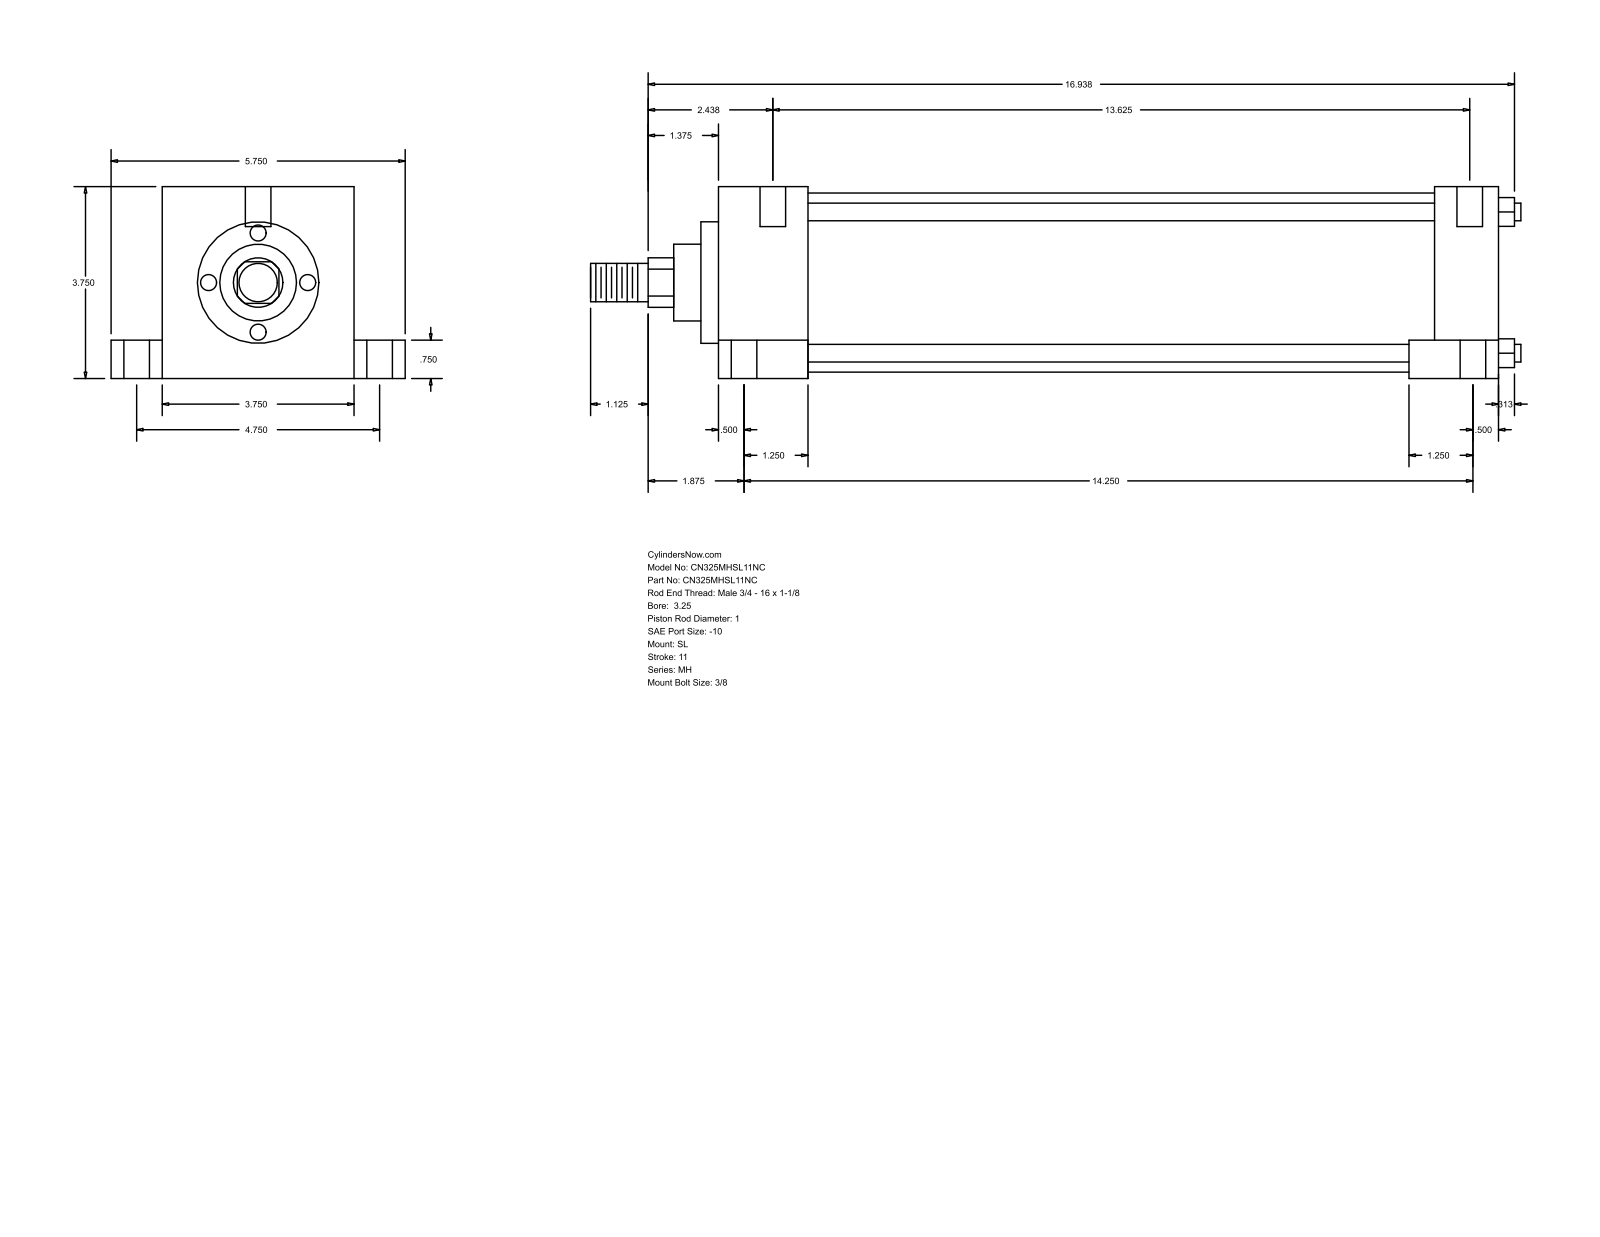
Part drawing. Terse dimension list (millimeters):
name: MH_SL__0325_1
written by: GSSL Pune (CONFIG_CONTROL_DESIGN)
unit: mm
bodies: 0 solids, 110 faces (77 planar, 33 cylindrical, 0 other)
size: 461.96 × 146.05 × 95.25
holes: 6× ⌀12.7, 4× ⌀5.56, 4× ⌀19.05
bosses: 4× ⌀8.76, 1× ⌀88.9, 1× ⌀60.33, 1× ⌀38.1, 1× ⌀25.4, 1× ⌀19.05
rounds: 1× R12.29
face distances: 95.24, 387.35, 44.46, 342.89, 25.41, 120.65, 19.05, 76.19, 355.6, 311.14
hole spacings: 60.35, 60.41, 61.65, 62, 120.66, 352.42, 352.86, 354.41
